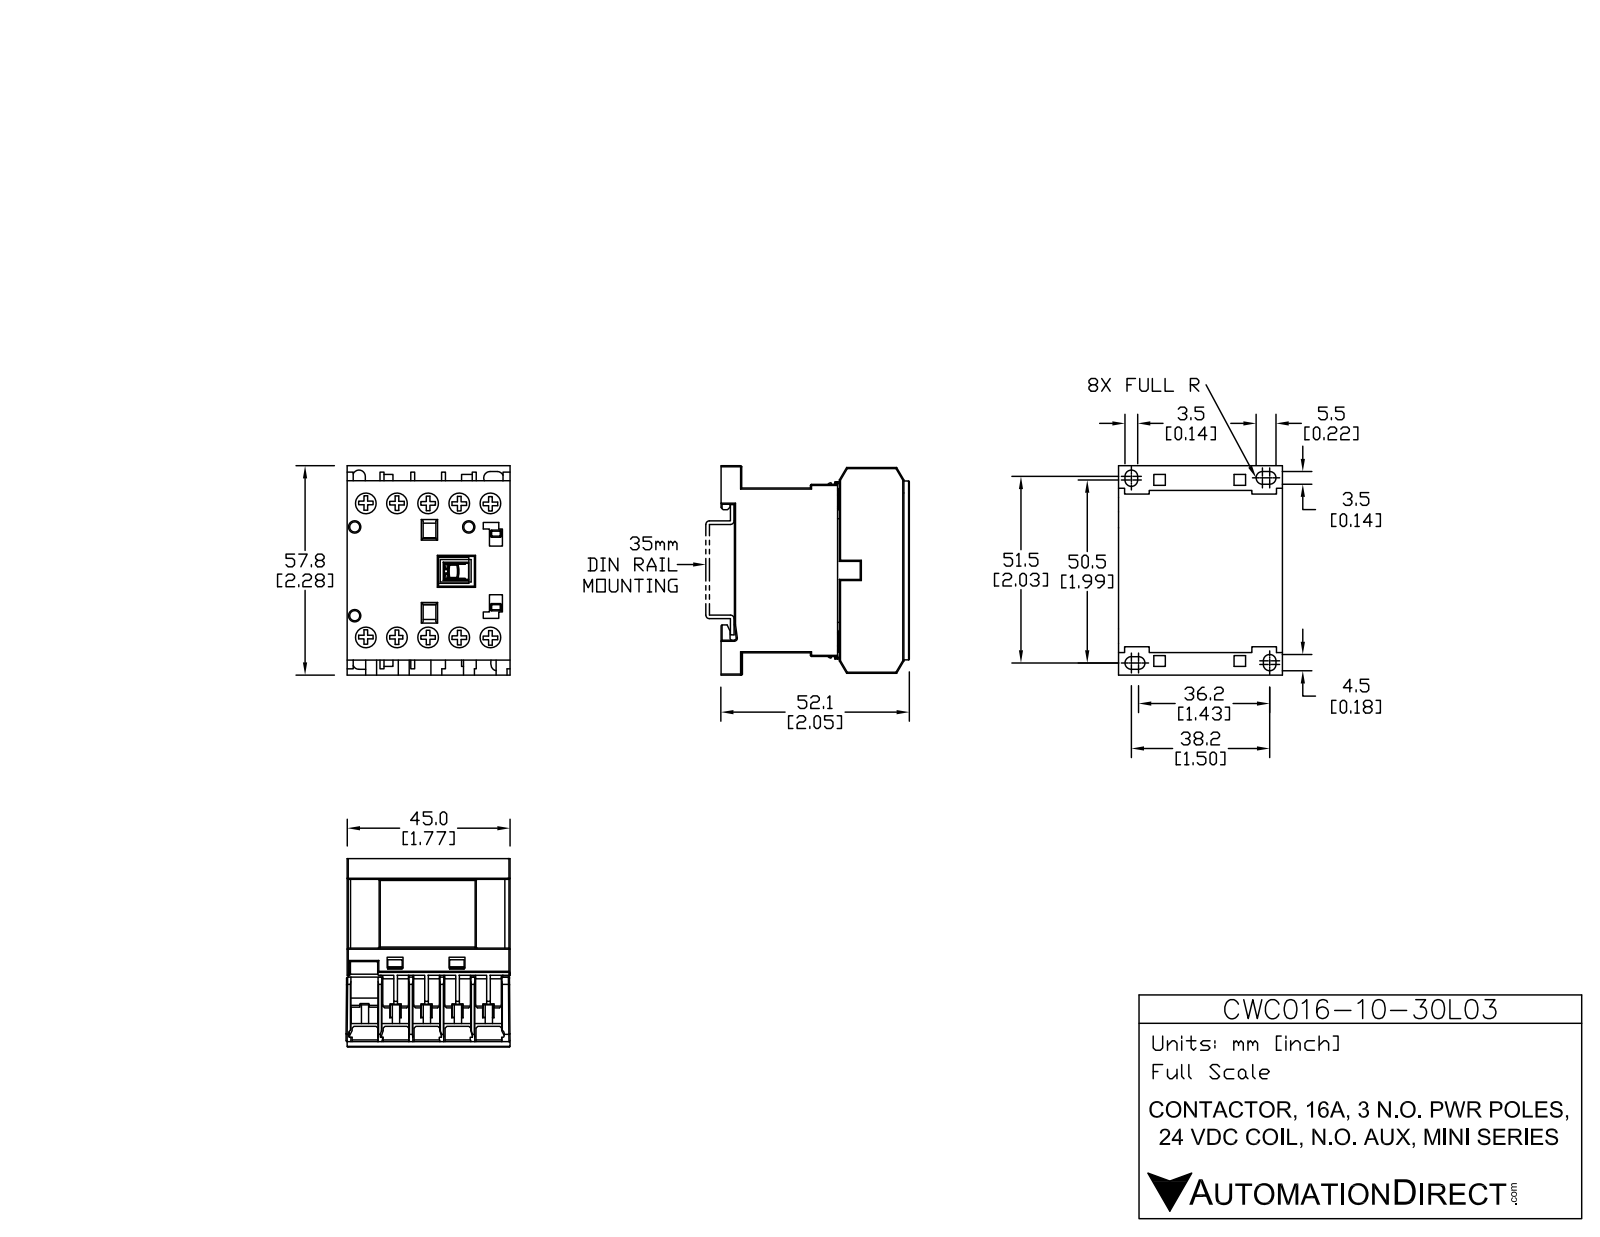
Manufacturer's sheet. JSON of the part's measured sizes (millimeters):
{"part_name": "CWC16-10-30L03", "step_written_by": "SolidWorks 2013 (AUTOMOTIVE_DESIGN)", "units": "millimeters", "bodies": {"solids": 15, "faces": 535, "planar": 445, "cylindrical": 90, "other": 0}, "overall_size": [58.04, 52.12, 45.75], "volume_mm3": 97133, "surface_area_mm2": 30437, "round_holes": [[6.2, 10], [2.8, 3]], "round_bosses_or_shafts": [[5.9, 10]], "partial_cylinders_radius": [[0.3, 20], [1.72, 6], [1.73, 2], [0.32, 1], [0.42, 1], [0.55, 1]], "face_to_face_distances": [8.25, 45.5, 1.25, 16.5, 9.5, 5.5, 17.75, 5.13, 10.63, 7], "hole_center_spacings": [8.55, 37.94, 17.1, 40.72, 36.96, 25.65, 44.99, 6.91]}
